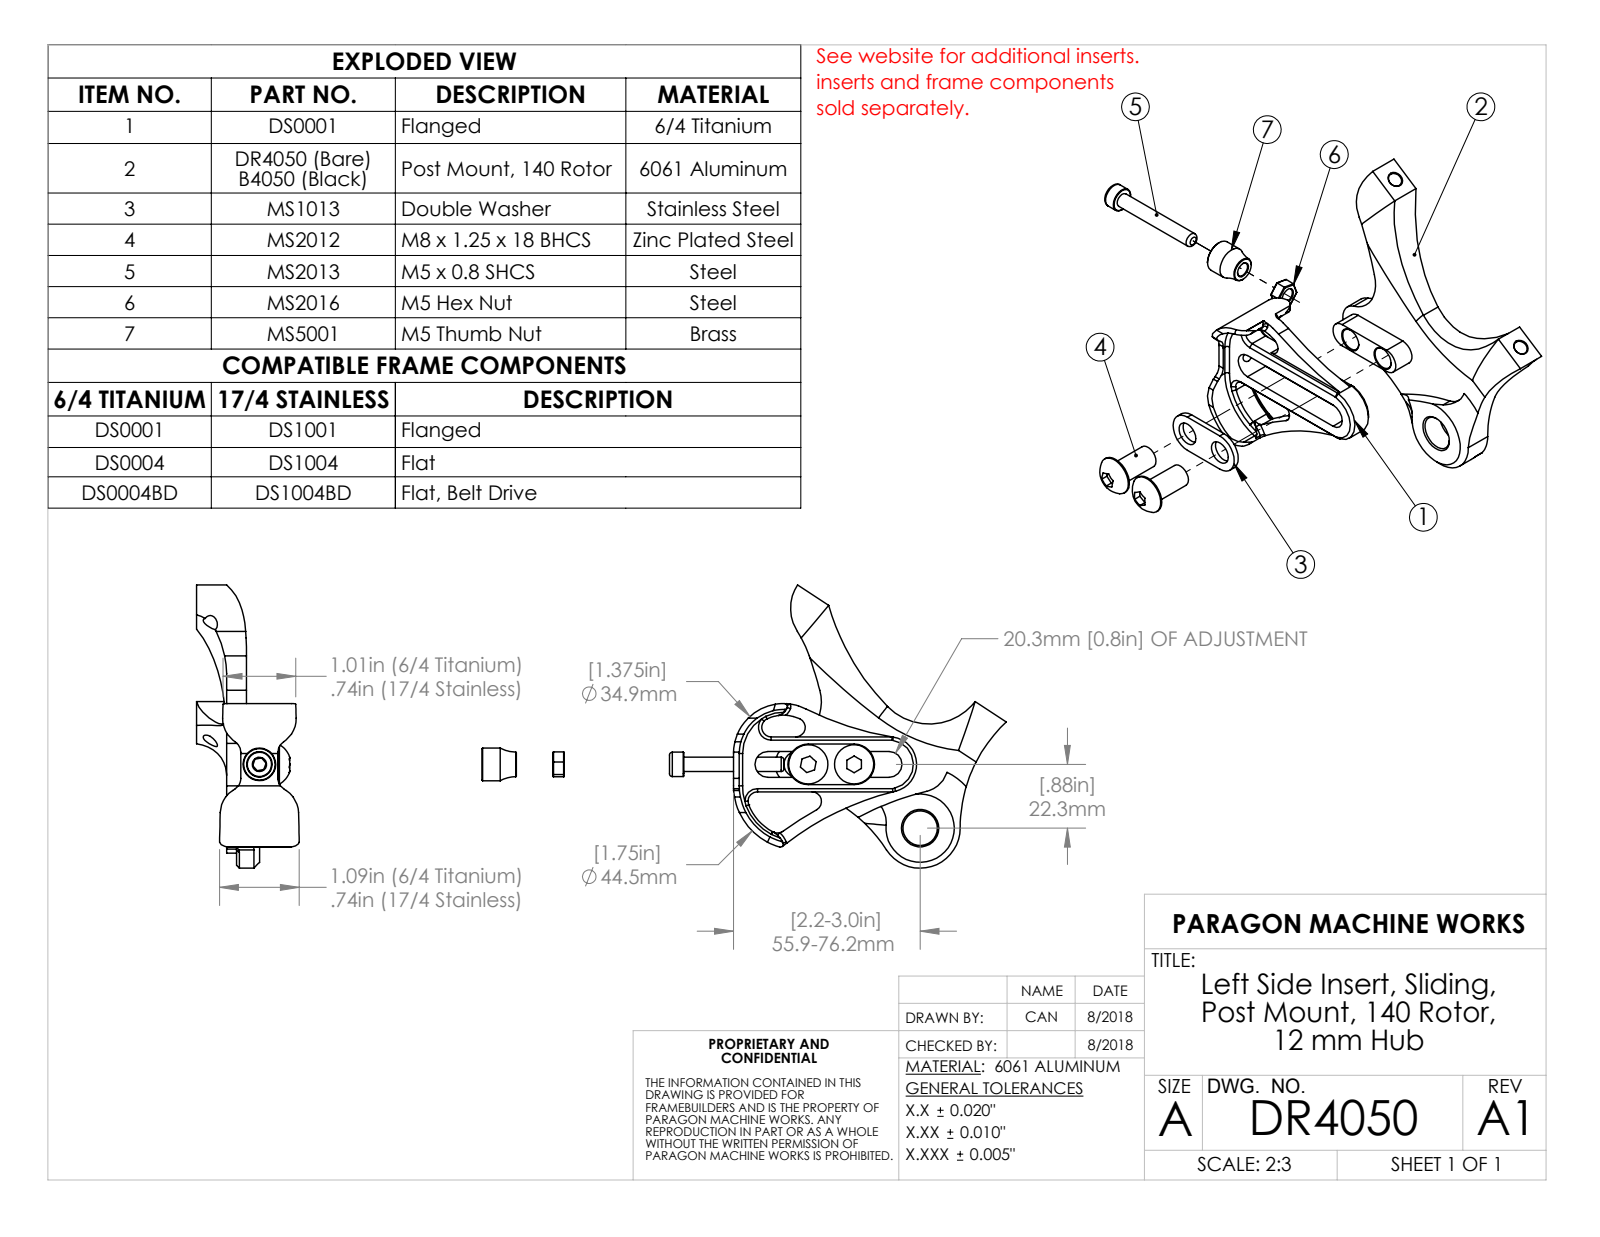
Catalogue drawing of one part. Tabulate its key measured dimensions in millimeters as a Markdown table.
| quantity | value |
| --- | --- |
| part name | DR4050 |
| STEP written by | SolidWorks 2023 (AUTOMOTIVE_DESIGN) |
| units | millimeters |
| bodies | 1 solid, 75 faces (13 planar, 37 cylindrical, 25 other) |
| overall size | 98.91 × 80.73 × 25.4 |
| volume | 26 413 mm³ |
| surface area | 11 168 mm² |
| round holes (diameter × count) | 5 × 2, 7.92 × 2, 12.04 × 1 |
| partial cylindrical surfaces (radius × count) | 1.25 × 2, 4.52 × 2, 15.24 × 2, 7.13 × 1, 7.62 × 1, 9.78 × 1, 10 × 1, 12.7 × 1 |
| main face-to-face distances | 6.96, 11.5, 4.54, 3.5, 3.46, 8, 10.49, 13.99, 17.45, 21.99 |
| hole center spacings | 16, 32.06, 44.96, 74.2 |
